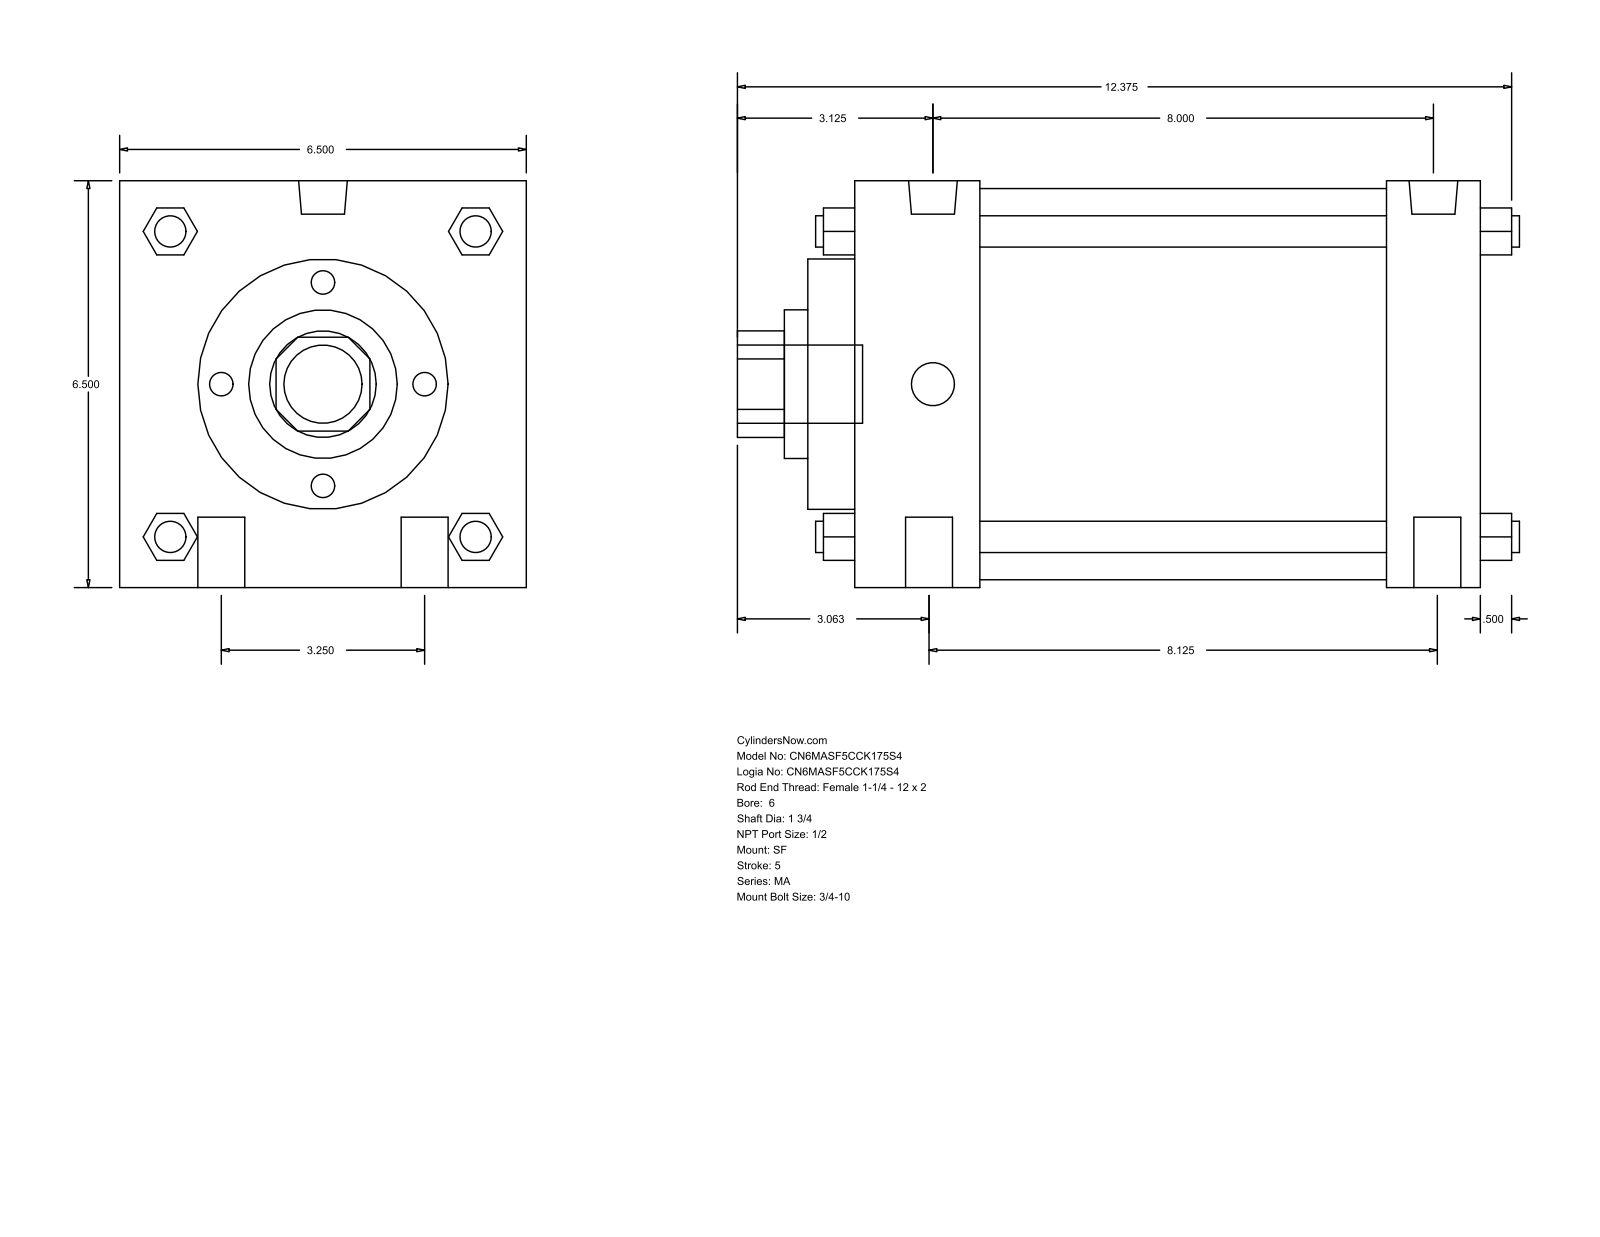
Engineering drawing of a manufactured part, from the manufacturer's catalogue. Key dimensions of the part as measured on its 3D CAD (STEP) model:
Part name (STEP PRODUCT): MA_SF__0600_1.75
STEP written by: GSSL Pune (CONFIG_CONTROL_DESIGN)
Units: millimetres
Bodies: 0 solids, 126 faces (95 planar, 31 cylindrical, 0 other)
Overall size (bounding box): 317.5 × 165.1 × 165.1
Round holes (diameter × count): ⌀44.45 ×1, ⌀60.33 ×1, ⌀101.6 ×1, ⌀158.75 ×1
Round bosses / shafts (diameter × count): ⌀19.05 ×4, ⌀12.7 ×4, ⌀19.77 ×2, ⌀17.46 ×2, ⌀31.75 ×1
Partial cylindrical surfaces — rounded edges, fillets, slot ends (radius × count): R21.63 ×1
Main face-to-face distances: 165.1, 254, 19.05, 50.8, 215.9, 38.1, 203.2, 69.85, 234.95, 273.05
